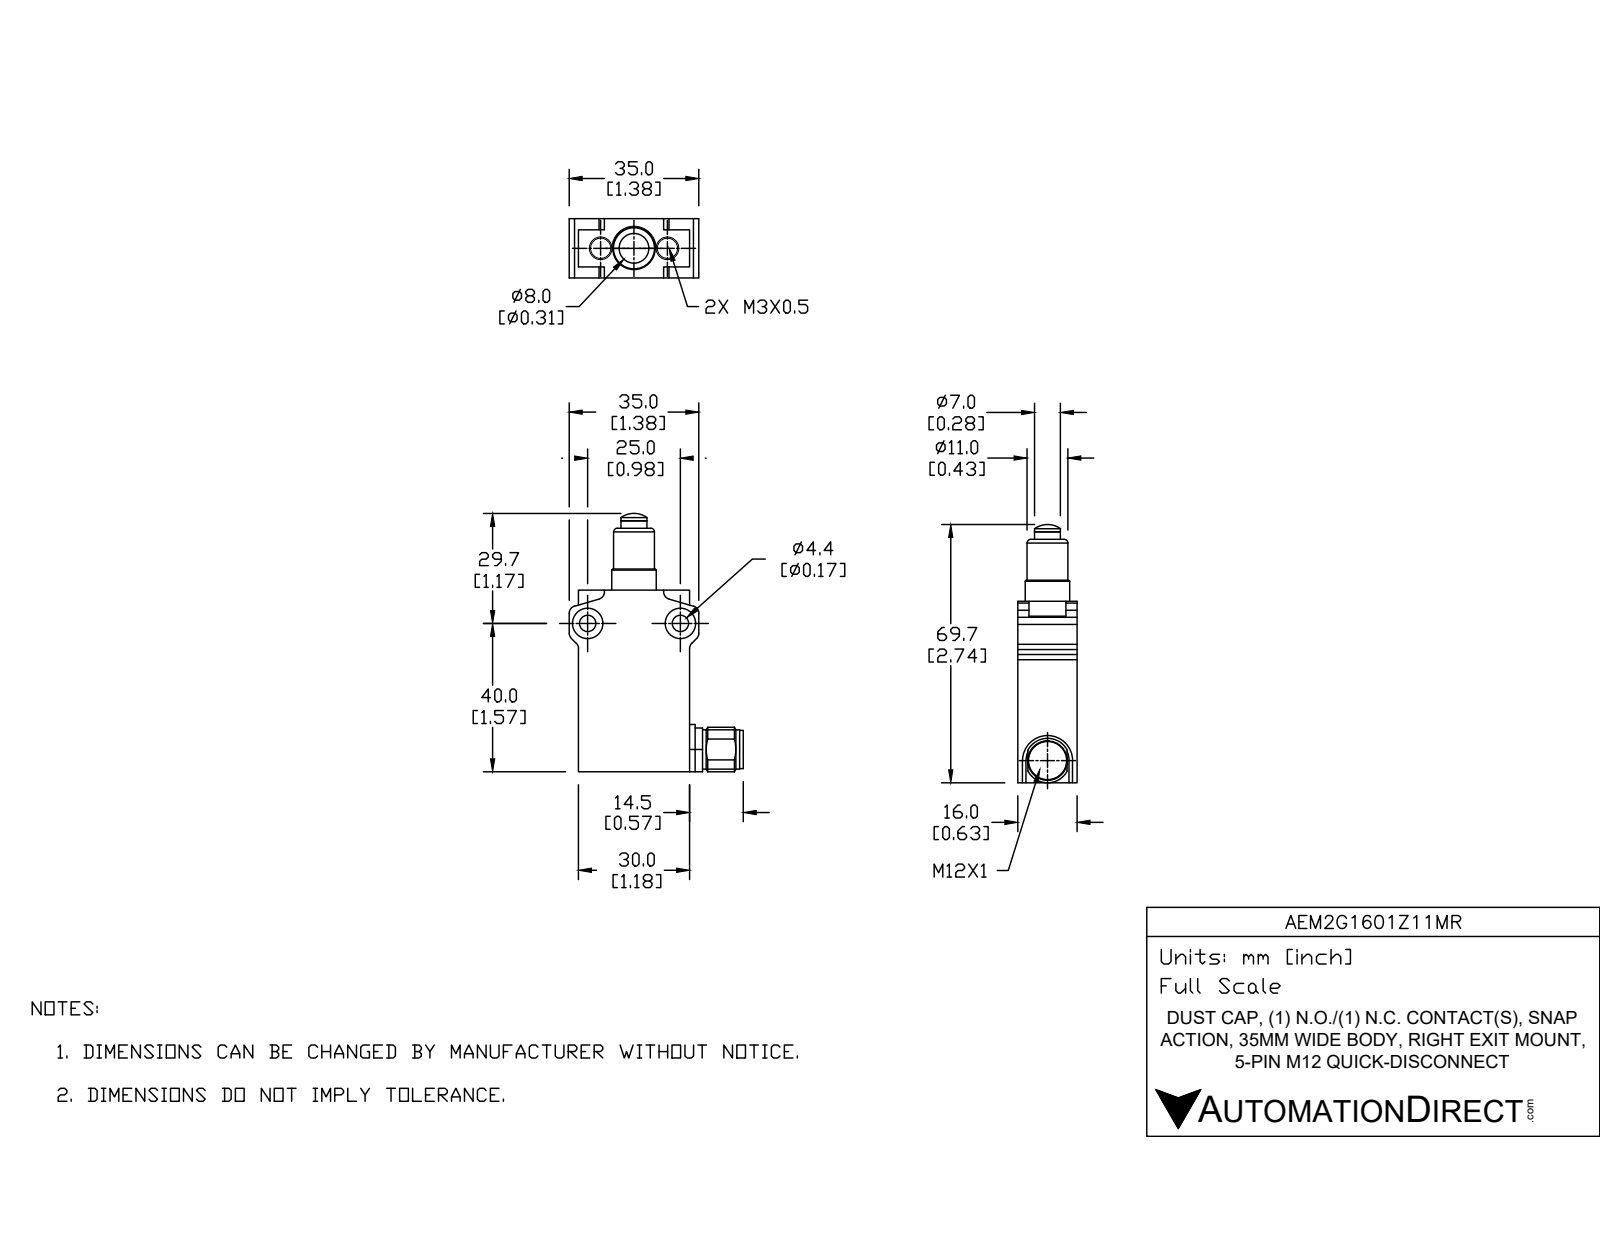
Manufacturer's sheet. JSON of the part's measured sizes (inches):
{"part_name": "AEM2G1601Z11MR", "step_written_by": "SolidWorks 2019 (AUTOMOTIVE_DESIGN)", "units": "inches", "bodies": {"solids": 4, "faces": 143, "planar": 56, "cylindrical": 52, "other": 35}, "overall_size": [2.862, 1.831, 0.63], "volume_in3": 1.667, "surface_area_in2": 14.86, "round_holes": [[0.118, 2], [0.173, 2], [0.323, 2], [0.197, 1], [0.28, 1]], "round_bosses_or_shafts": [[0.472, 2], [0.433, 1], [0.417, 1], [0.406, 1], [0.276, 1]], "partial_cylinders_radius": [[0.079, 8], [0.256, 1]], "face_to_face_distances": [0.63, 1.181, 2.047, 0.472, 1.858, 0.189, 0.098, 1.28, 0.157, 0.039], "hole_center_spacings": [0.374, 0.748, 0.984]}
